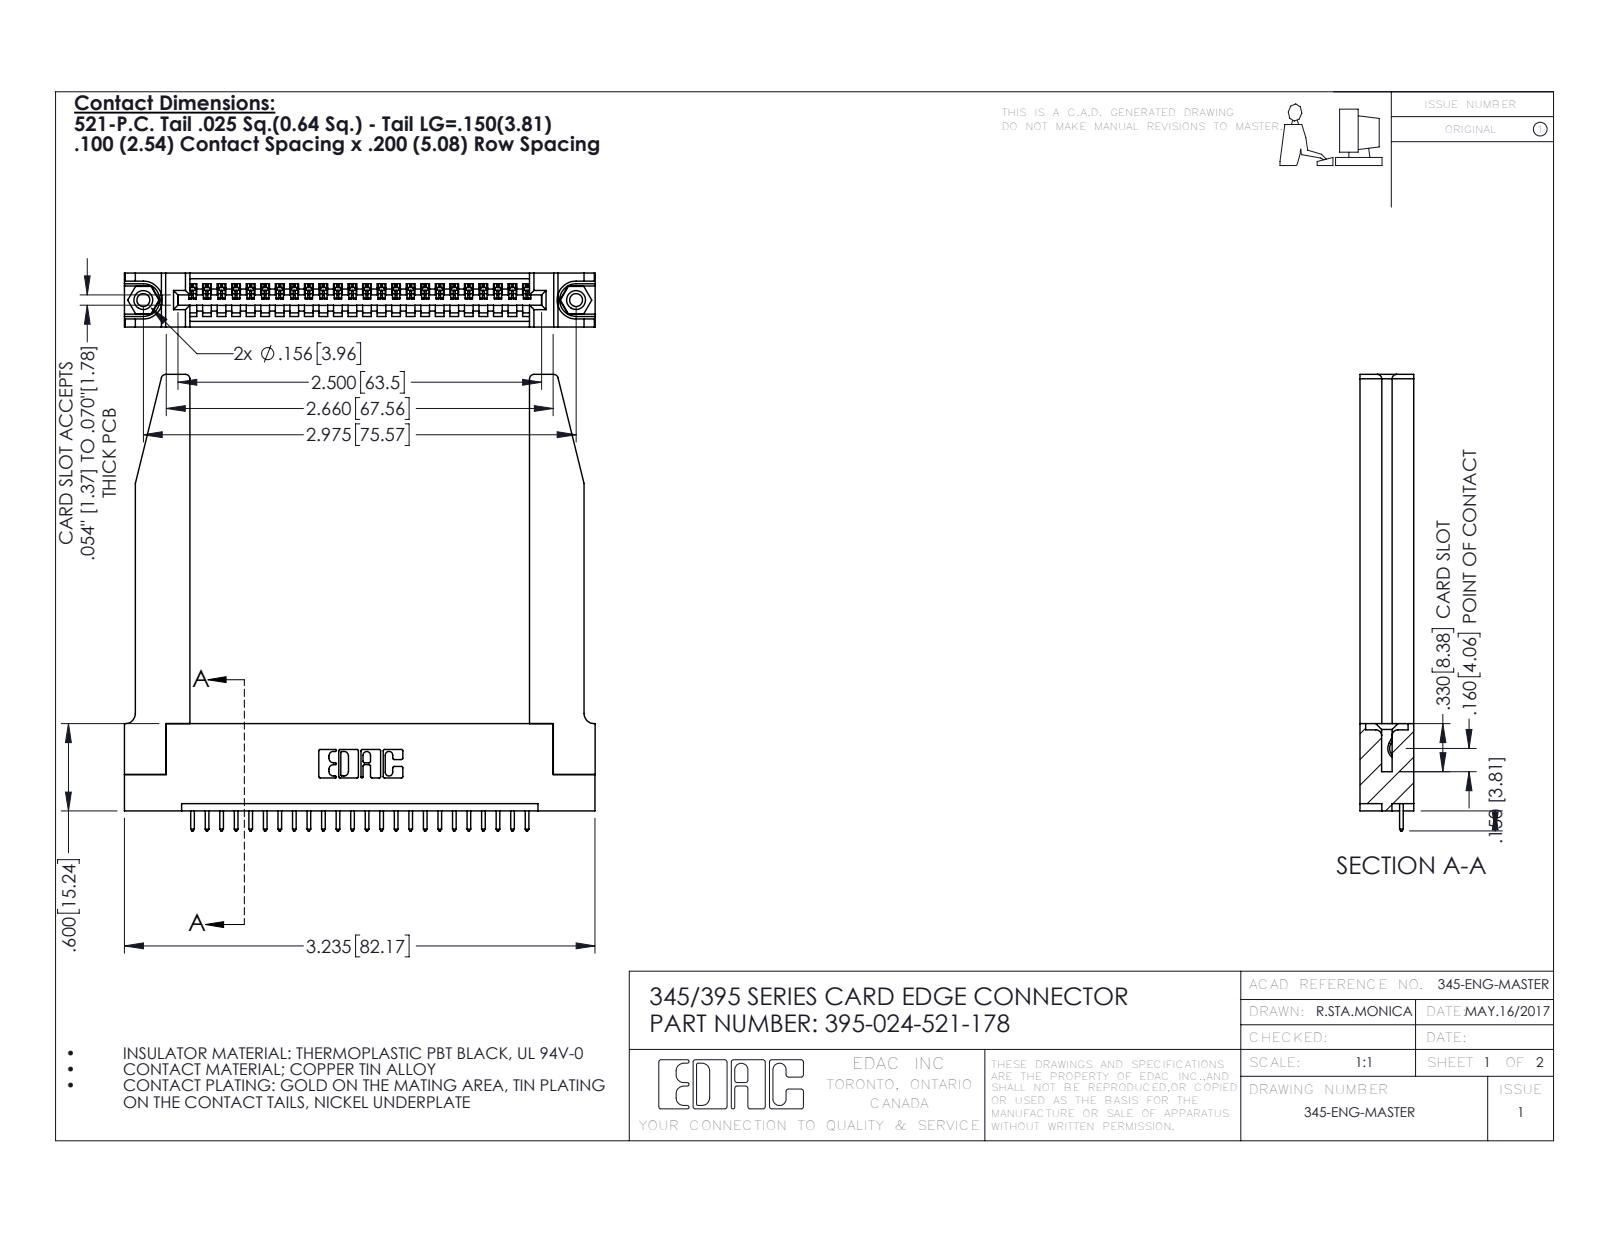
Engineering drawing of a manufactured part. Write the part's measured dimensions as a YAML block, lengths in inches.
part_name: "345-292-001_345-293-121; 395-024-521-178; 345-250-001_345-250-001-102; 345-220-078_345-220-078 (+1 more)"
step_written_by: "SolidWorks 2016 (CONFIG_CONTROL_DESIGN)"
units: inches
bodies: {solids: 29, faces: 1752, planar: 1182, cylindrical: 518, other: 52}
overall_size: [3.236, 3.137, 0.37]
volume: 0.937
surface_area: 25.45
round_holes:
  - {diameter: 0.089, count: 2}
  - {diameter: 0.125, count: 2}
  - {diameter: 0.156, count: 2}
  - {diameter: 0.064, count: 1}
round_bosses_or_shafts:
  - {diameter: 0.155, count: 2}
partial_cylinders:
  - {radius: 0.006, count: 48}
  - {radius: 0.01, count: 48}
  - {radius: 0.01, count: 22}
  - {radius: 0.03, count: 8}
  - {radius: 0.007, count: 6}
  - {radius: 0.031, count: 6}
  - {radius: 0.026, count: 3}
  - {radius: 0.031, count: 2}
face_to_face_distances: [0.37, 0.072, 0.298, 0.2, 0.098, 0.272, 0.025, 0.148, 0.15, 0.077]
hole_center_spacings: [0.27, 2.741, 2.975]
